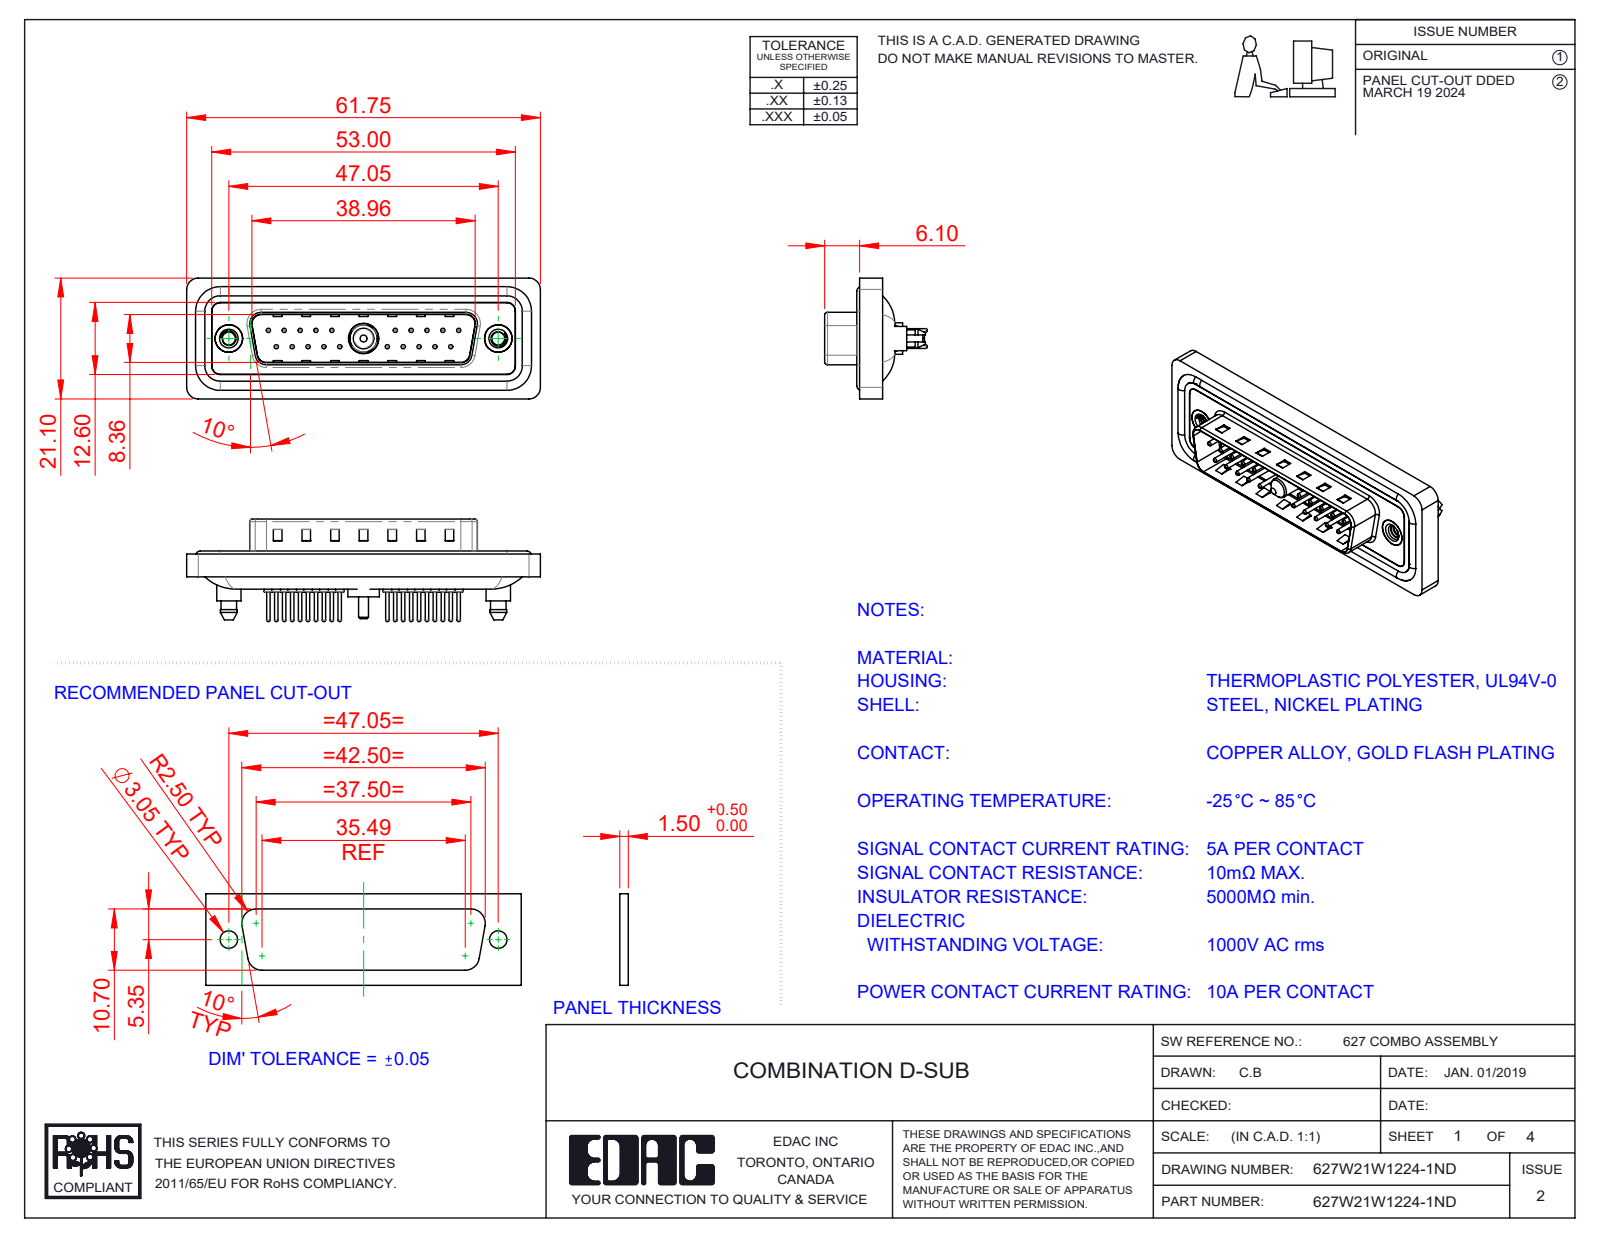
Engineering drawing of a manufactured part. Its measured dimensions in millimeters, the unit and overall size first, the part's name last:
Units: millimetres
Overall size (bounding box): 61.75 × 21.1 × 17.9
Round holes (diameter × count): ⌀0.75 ×20, ⌀1.6 ×20, ⌀2 ×20, ⌀2.26 ×2, ⌀4 ×2, ⌀4.8 ×2, ⌀5 ×2, ⌀4.85 ×1, ⌀5.3 ×1
Round bosses / shafts (diameter × count): ⌀1.5 ×20, ⌀0.6 ×20, ⌀1.6 ×4, ⌀5.4 ×2, ⌀4.9 ×2, ⌀4.25 ×2, ⌀5.5 ×1, ⌀5.2 ×1
Partial cylindrical surfaces — rounded edges, fillets, slot ends (radius × count): R1.5 ×24, R2 ×18, R1.6 ×10, R0.5 ×8, R0.25 ×4, R0.6 ×4, R0.65 ×4, R0.9 ×4
Main face-to-face distances: 0.4, 1.5, 1.1, 1.6, 0.5, 3.1, 2.9, 4.1, 0.82, 9.58
Hole centre spacings: 3.16, 2.77, 5.54, 8.31, 5.04, 19.39, 20.97, 22.16
Volume: 7 317 mm³ · Surface area: 12 277 mm²
Bodies: 29 solids, 1320 faces (375 planar, 527 cylindrical, 418 other)
Part name (STEP PRODUCT): 627Combo Contact Row 1_24; 627Combo Housing_21W1; 627Combo Threaded Boardlock_D; 627Combo Shell Rear_25 Contacts (+6 more)
STEP written by: SolidWorks 2023 (CONFIG_CONTROL_DESIGN)
